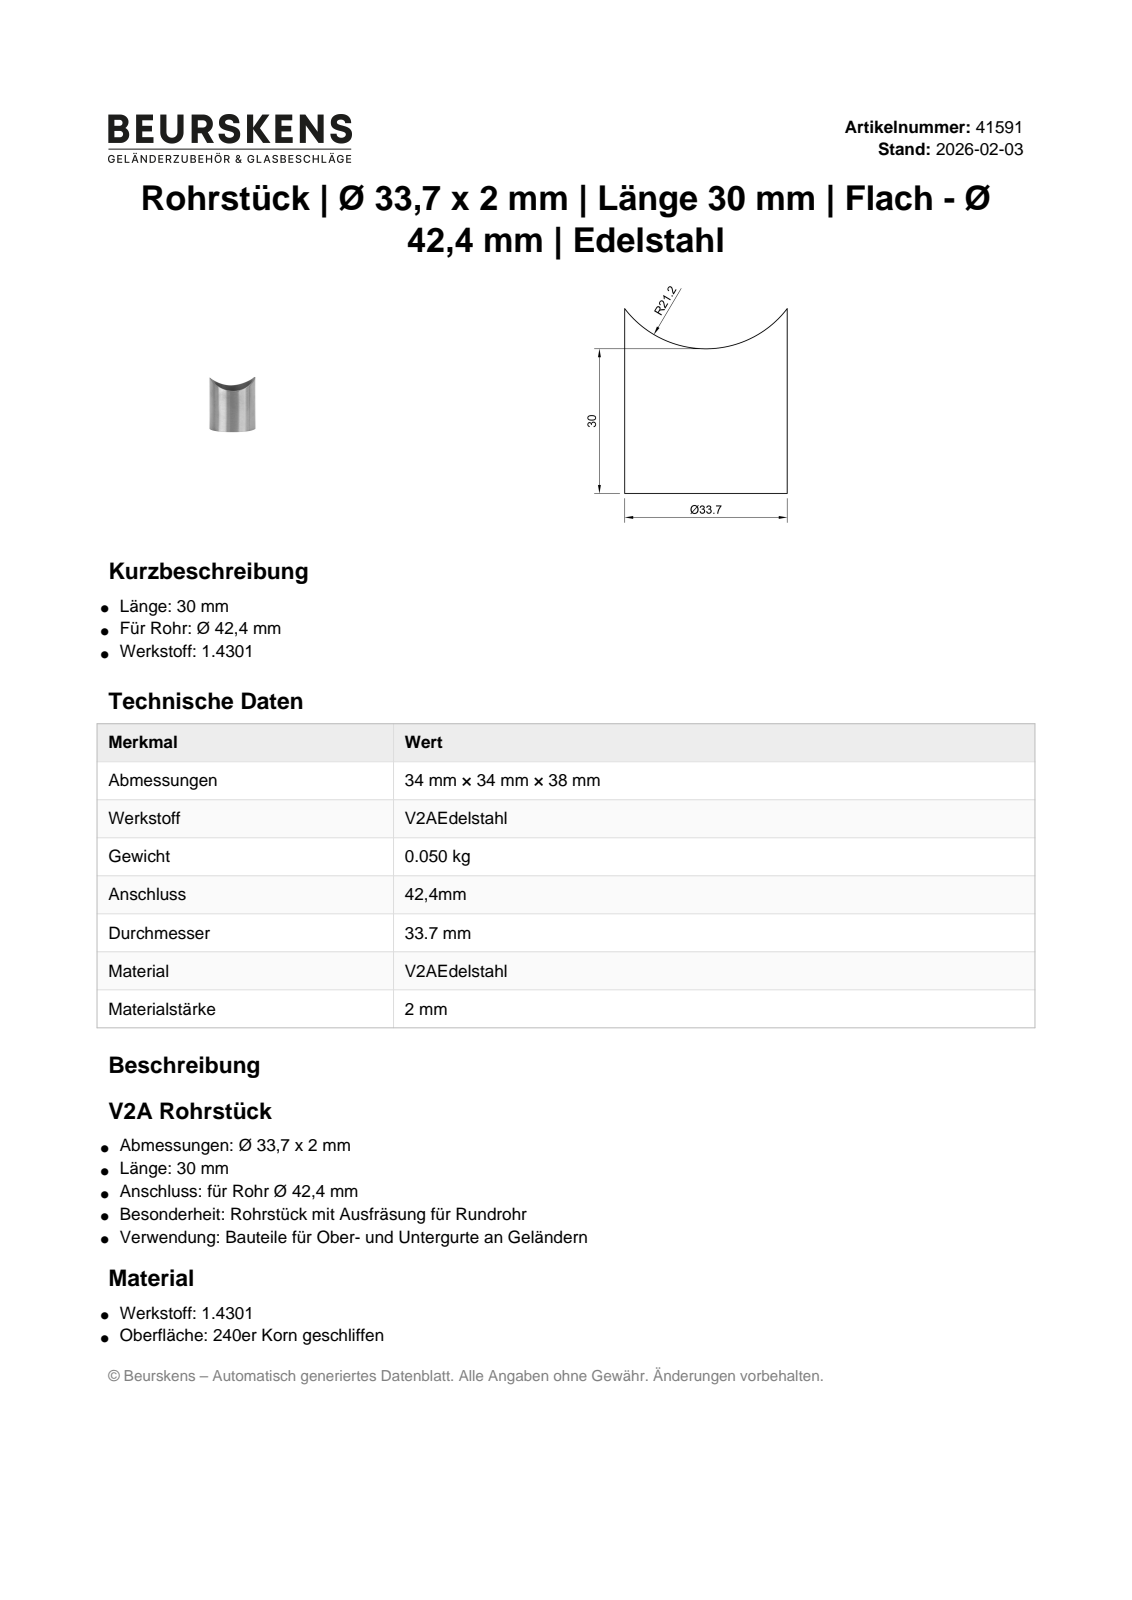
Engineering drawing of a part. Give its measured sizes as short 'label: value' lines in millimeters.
name: 41591
written by: Autodesk Inventor 2022 (AUTOMOTIVE_DESIGN)
unit: mm
bodies: 1 solid, 4 faces (1 planar, 3 cylindrical, 0 other)
size: 38.34 × 33.7 × 33.7
volume: 3 454 mm³; area: 7 145 mm²
holes: 1× ⌀31.7
bosses: 1× ⌀33.7
rounds: 1× R21.2
